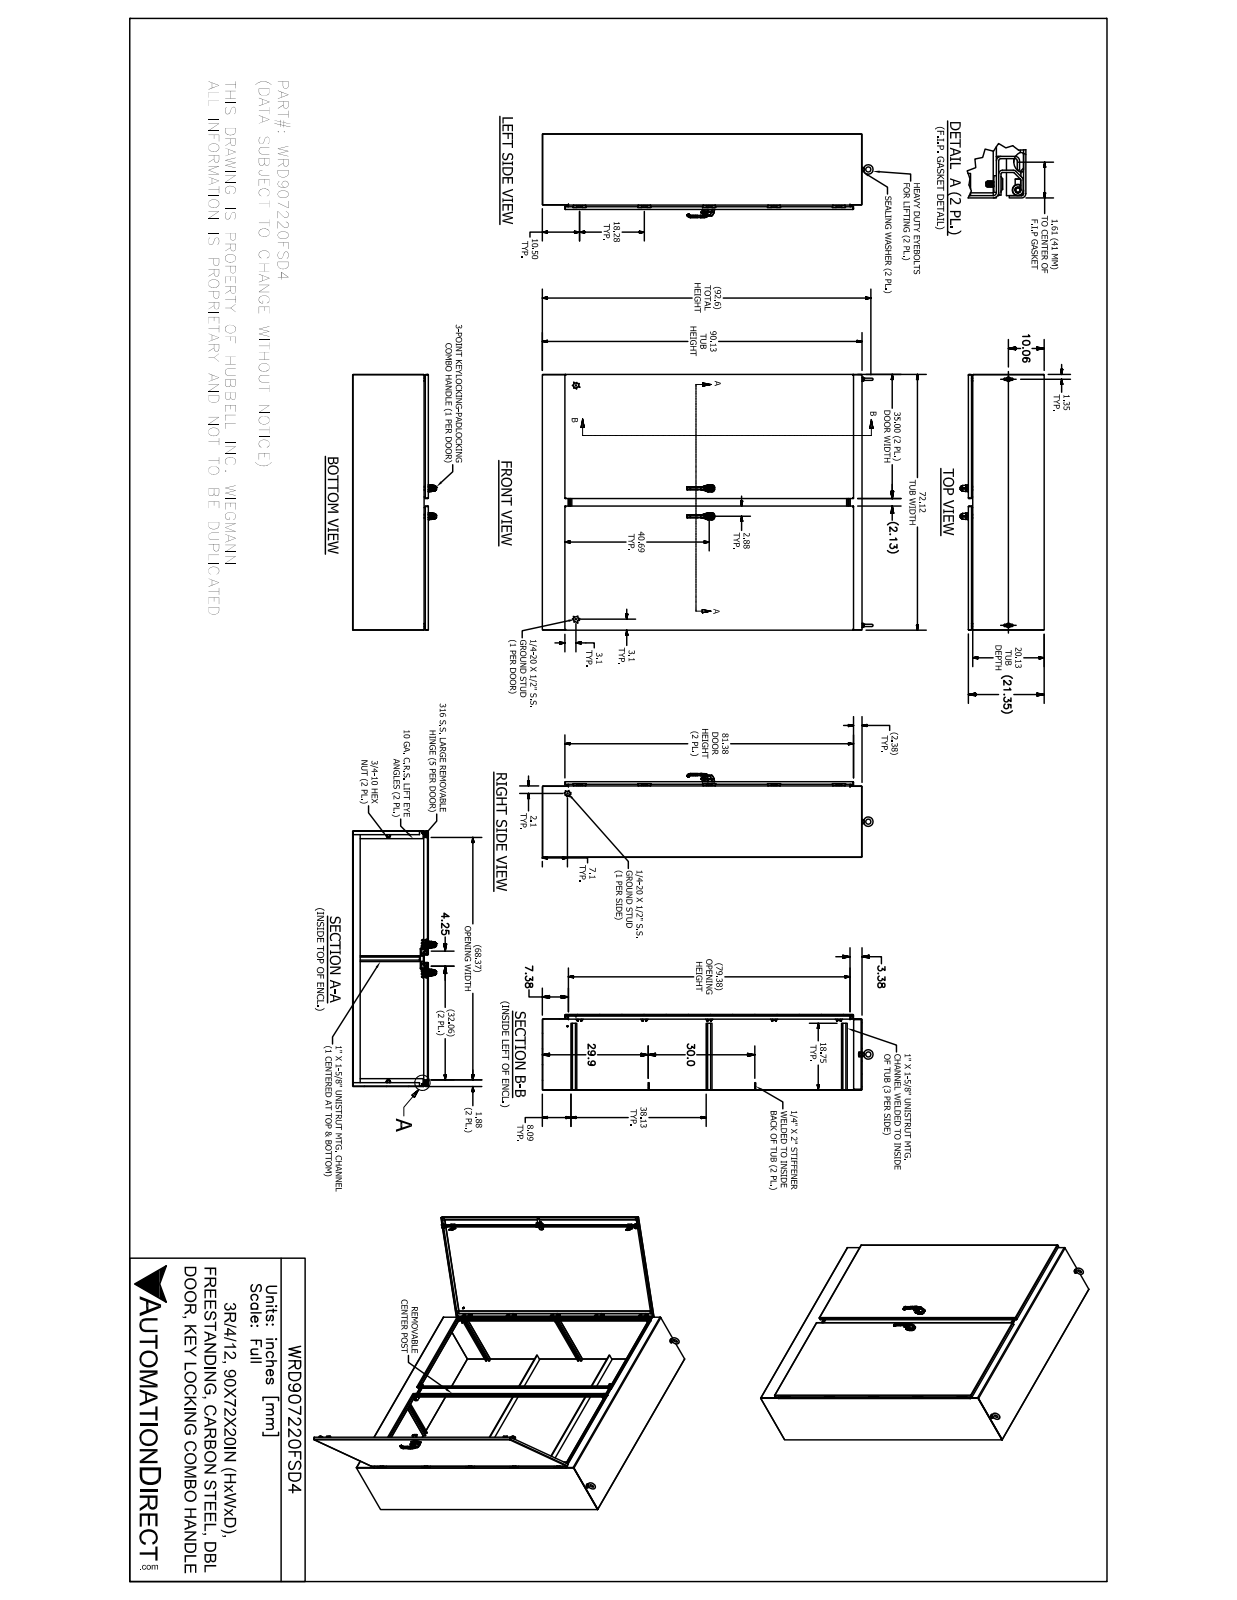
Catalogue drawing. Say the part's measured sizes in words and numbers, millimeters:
The part is named "WRD907220FSD4". Its 3-D file was written by "SolidWorks 2017 (AUTOMOTIVE_DESIGN)". It is 170 solids with 3566 faces: 1652 planar, 1192 cylindrical and 722 other. Overall it measures 2368.5 by 1832.2 by 597.6 millimeters. Its volume is 42 130 000 cubic millimeters and its surface area 30 330 000 square millimeters. Round holes: 24 of diameter 6.8, 20 of diameter 5.8, 20 of diameter 7.1, 20 of diameter 16.5, 8 of diameter 5.1, 8 of diameter 7, 6 of diameter 7.1, 4 of diameter 4, 4 of diameter 6.4, 4 of diameter 10.2, 4 of diameter 11.4, 3 of diameter 6.1. Round bosses or shafts: 17 of diameter 15.9, 14 of diameter 6.4, 4 of diameter 13.5, 4 of diameter 11.1, 4 of diameter 9.5, 4 of diameter 8, 4 of diameter 5.4, 3 of diameter 25.4. Partial cylindrical surfaces (rounded edges, fillets, slot ends): 47 of radius 1.6, 36 of radius 3.2, 32 of radius 1.3, 25 of radius 1.6, 20 of radius 0.3, 16 of radius 0.5, 16 of radius 0.6, 16 of radius 1.3. The main face-to-face distances are 2.6, 539.6, 537, 542.3, 1829.3, 2286.5, 1826.7, 1832, 505.9, 33.7. The hole center spacings are 1859.2, 464.3, 25.4, 1800.2, 1800.4, 928.7, 1393, 1853.
